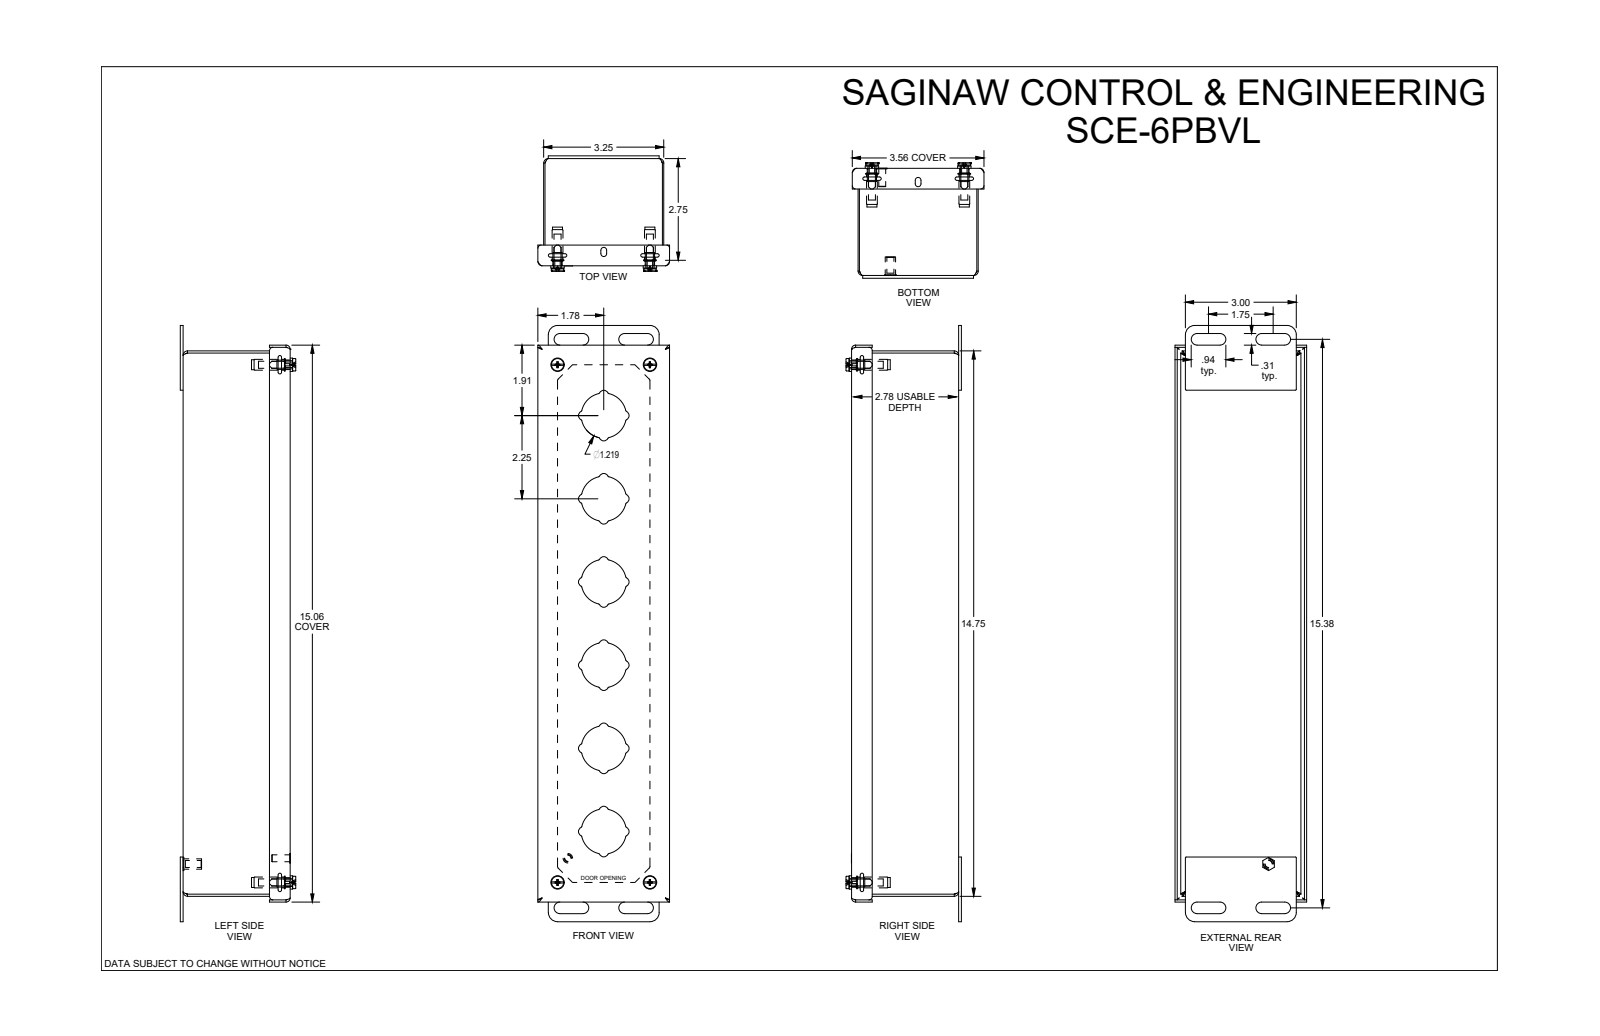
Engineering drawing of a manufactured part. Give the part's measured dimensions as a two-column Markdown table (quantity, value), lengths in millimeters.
| quantity | value |
| --- | --- |
| part name | SCE-6PBVL |
| STEP written by | SolidWorks 2021 (AUTOMOTIVE_DESIGN) |
| units | millimeters |
| bodies | 3 solids, 512 faces (153 planar, 275 cylindrical, 84 other) |
| overall size | 409.6 × 90.5 × 77.1 |
| volume | 242 000 mm³ |
| surface area | 309 900 mm² |
| round holes (diameter × count) | 4.8 × 5, 5.6 × 4, 6.4 × 4, 6.8 × 4, 8.1 × 4 |
| round bosses / shafts (diameter × count) | 9.2 × 4, 8.6 × 4, 7.4 × 4, 6.9 × 4, 6.6 × 4, 7.1 × 1, 6.5 × 1, 4.8 × 1 |
| partial cylindrical surfaces (radius × count) | 1 × 48, 3.2 × 24, 1.5 × 20, 0.4 × 8, 2.9 × 8, 4 × 8, 6.2 × 8, 15.5 × 6 |
| main face-to-face distances | 1.5, 72.1, 81, 70.6, 73.6, 82.6, 79.5, 4, 85, 68.3 |
| hole center spacings | 63.5, 355.6, 355.6, 361.2, 361.2, 63.5, 63.5, 361.1 |
